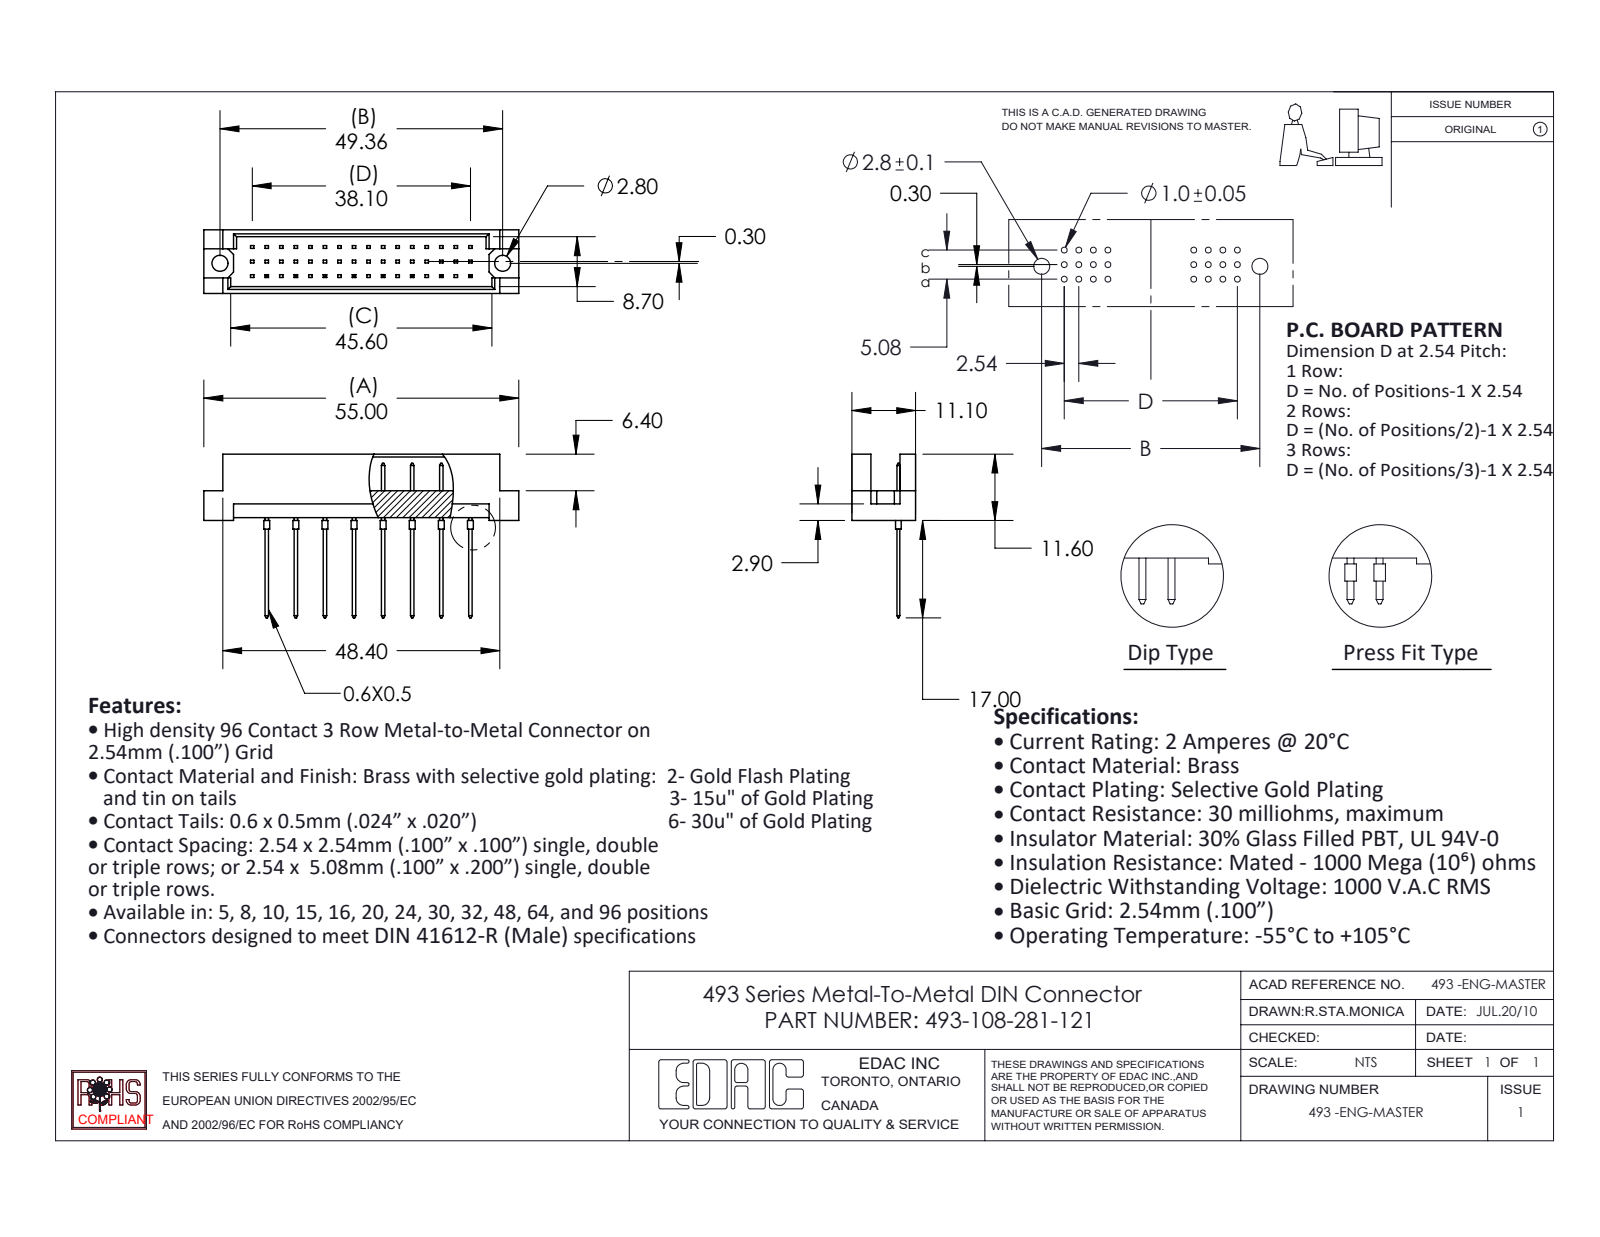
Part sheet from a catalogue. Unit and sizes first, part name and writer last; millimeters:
Units: millimetres
Overall size (bounding box): 55 × 28.6 × 11.1
Round holes (diameter × count): ⌀2.8 ×2
Round bosses / shafts (diameter × count): ⌀1 ×8
Main face-to-face distances: 1.2, 9.9, 11.1, 8.7, 5.08, 4.7, 0.5, 10.16, 2.76, 8.34
Hole centre spacings: 49.36
Volume: 3 342 mm³ · Surface area: 4 248 mm²
Bodies: 9 solids, 420 faces (400 planar, 20 cylindrical, 0 other)
Part name (STEP PRODUCT): 493-290_81; 493 Part_48; 493-108-281-122
STEP written by: SolidWorks 2020 (CONFIG_CONTROL_DESIGN)
